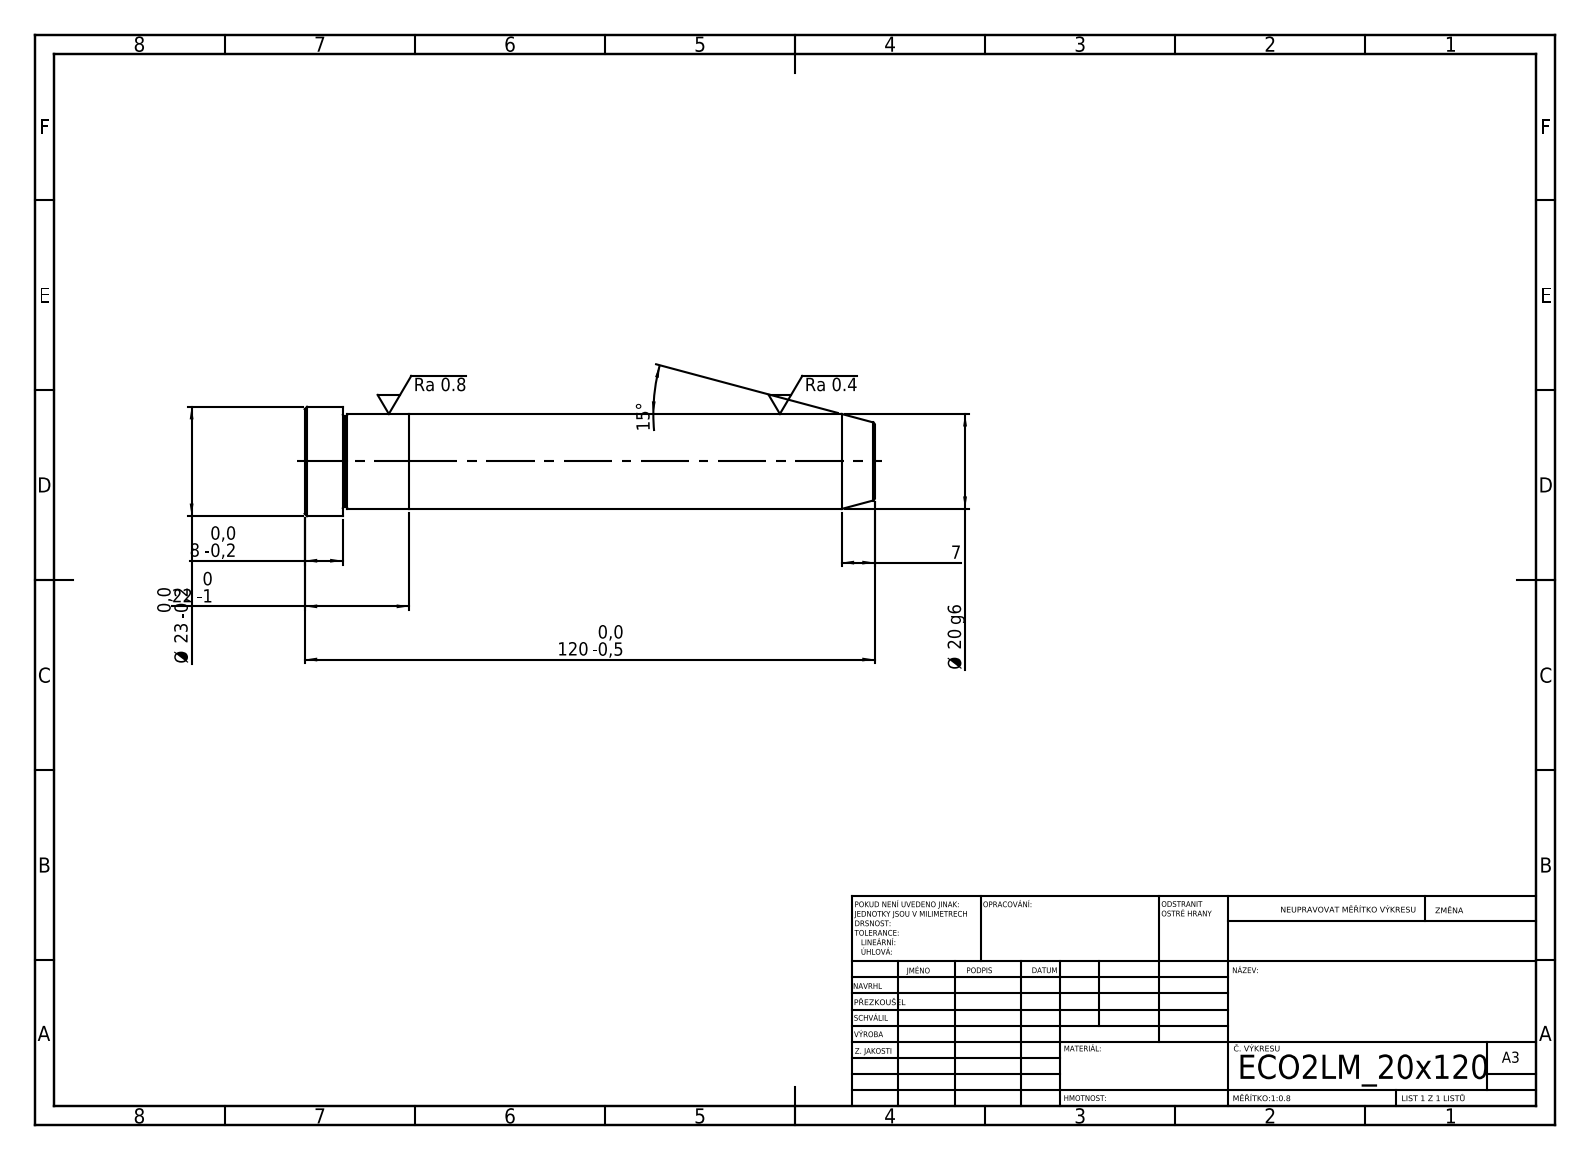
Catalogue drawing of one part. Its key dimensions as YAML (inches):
step_written_by: "SolidWorks 2019 (CONFIG_CONTROL_DESIGN)"
units: inches
bodies: {solids: 2, faces: 21, planar: 5, cylindrical: 6, other: 10}
overall_size: [4.724, 0.906, 0.906]
volume: 2.324
surface_area: 13.87
round_bosses_or_shafts:
  - {diameter: 0.906, count: 1}
  - {diameter: 0.787, count: 1}
face_to_face_distances: [0.866, 3.858, 4.724, 4.409, 0.551, 0.315]
